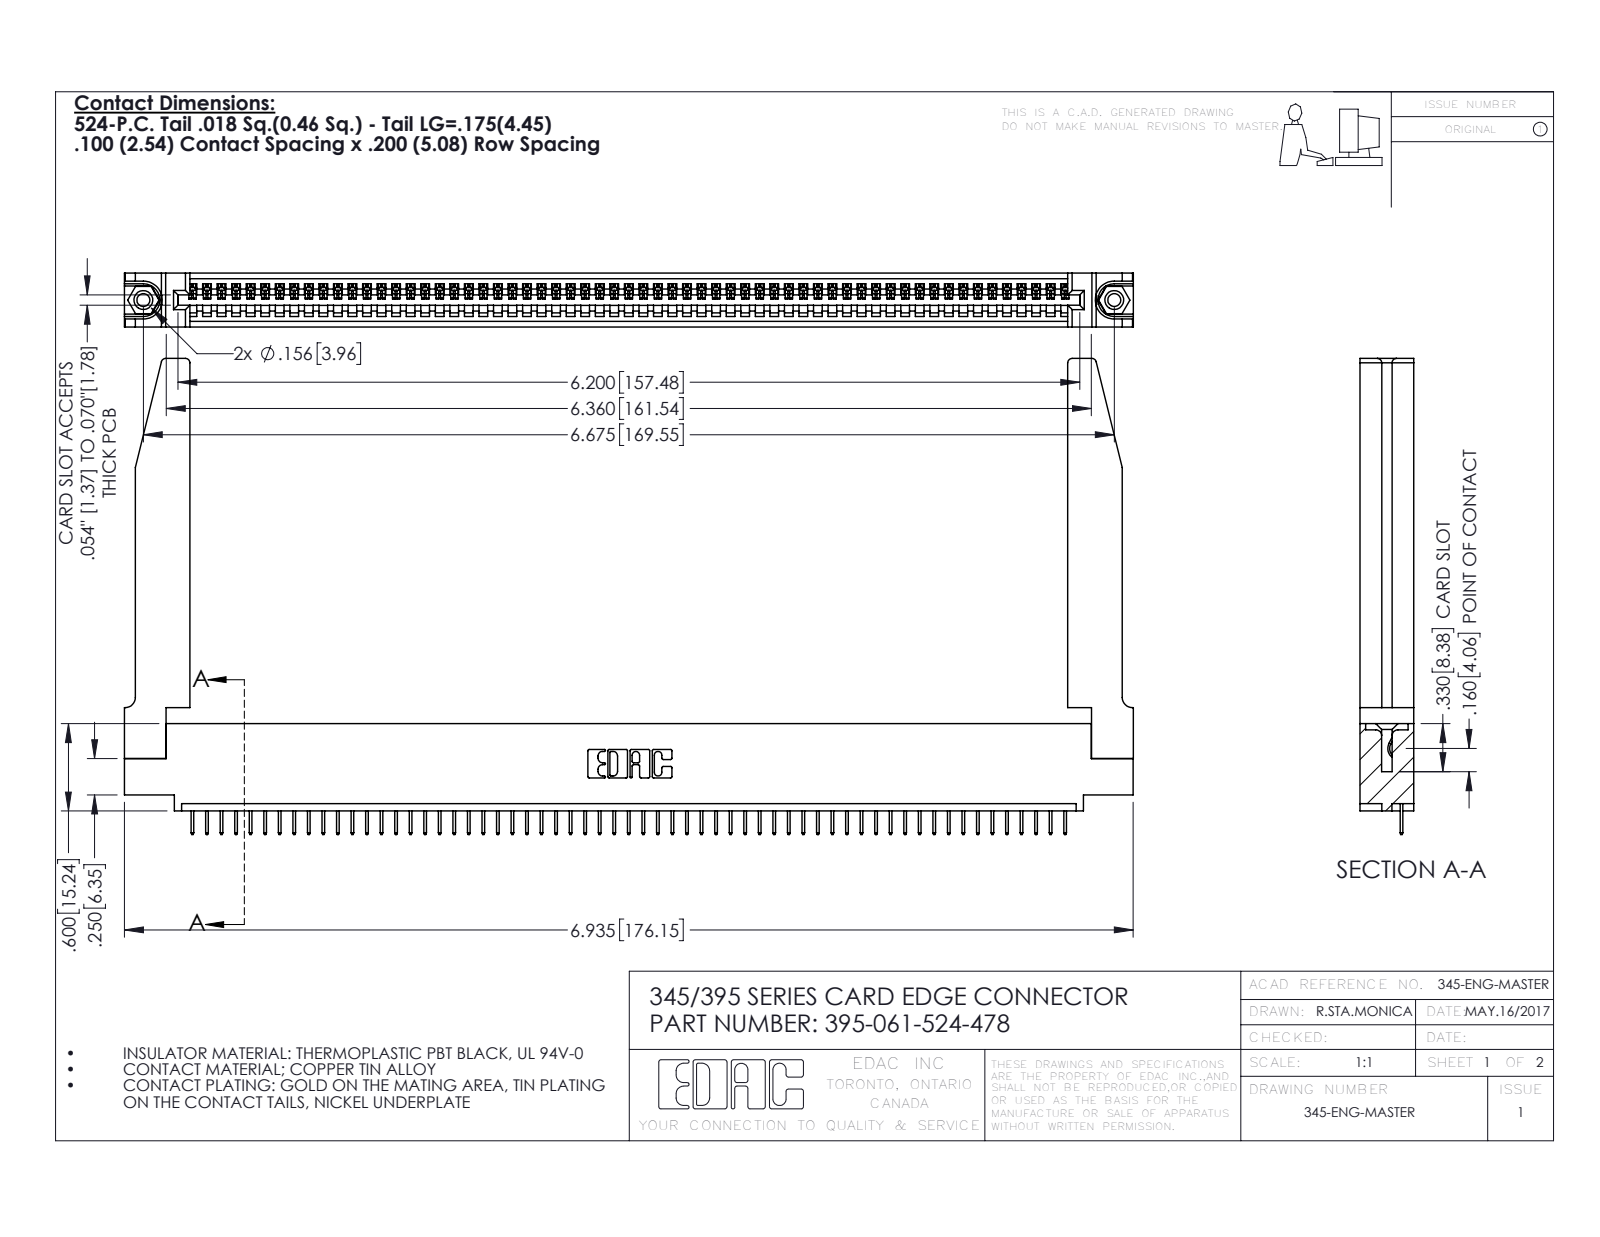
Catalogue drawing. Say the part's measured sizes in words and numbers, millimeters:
The part is named "345 Part_0.110 Offset - 0.156 Dia-TH; 395-061-524-478; 345-250-001_345-250-001-102; 345-220-078_345-220-078 (+1 more)". Its 3-D file was written by "SolidWorks 2016 (CONFIG_CONTROL_DESIGN)". It is 66 solids with 4146 faces: 3032 planar, 1062 cylindrical and 52 other. Overall it measures 176.2 by 83.1 by 9.4 millimeters. Its volume is 24 350 cubic millimeters and its surface area 28 440 square millimeters. Round holes: 2 of diameter 2.3, 2 of diameter 3.2, 2 of diameter 4, 1 of diameter 1.6. Round bosses or shafts: 2 of diameter 3.9. Partial cylindrical surfaces (rounded edges, fillets, slot ends): 122 of radius 0.2, 22 of radius 0.3, 8 of radius 0.8, 6 of radius 0.2, 6 of radius 0.8, 3 of radius 0.7, 2 of radius 0.8, 2 of radius 1. The main face-to-face distances are 9.4, 1.8, 7.6, 2.5, 6.9, 0.6, 5.1, 5.7, 1.8, 3.8. The hole center spacings are 6.9, 163.6, 169.5.
